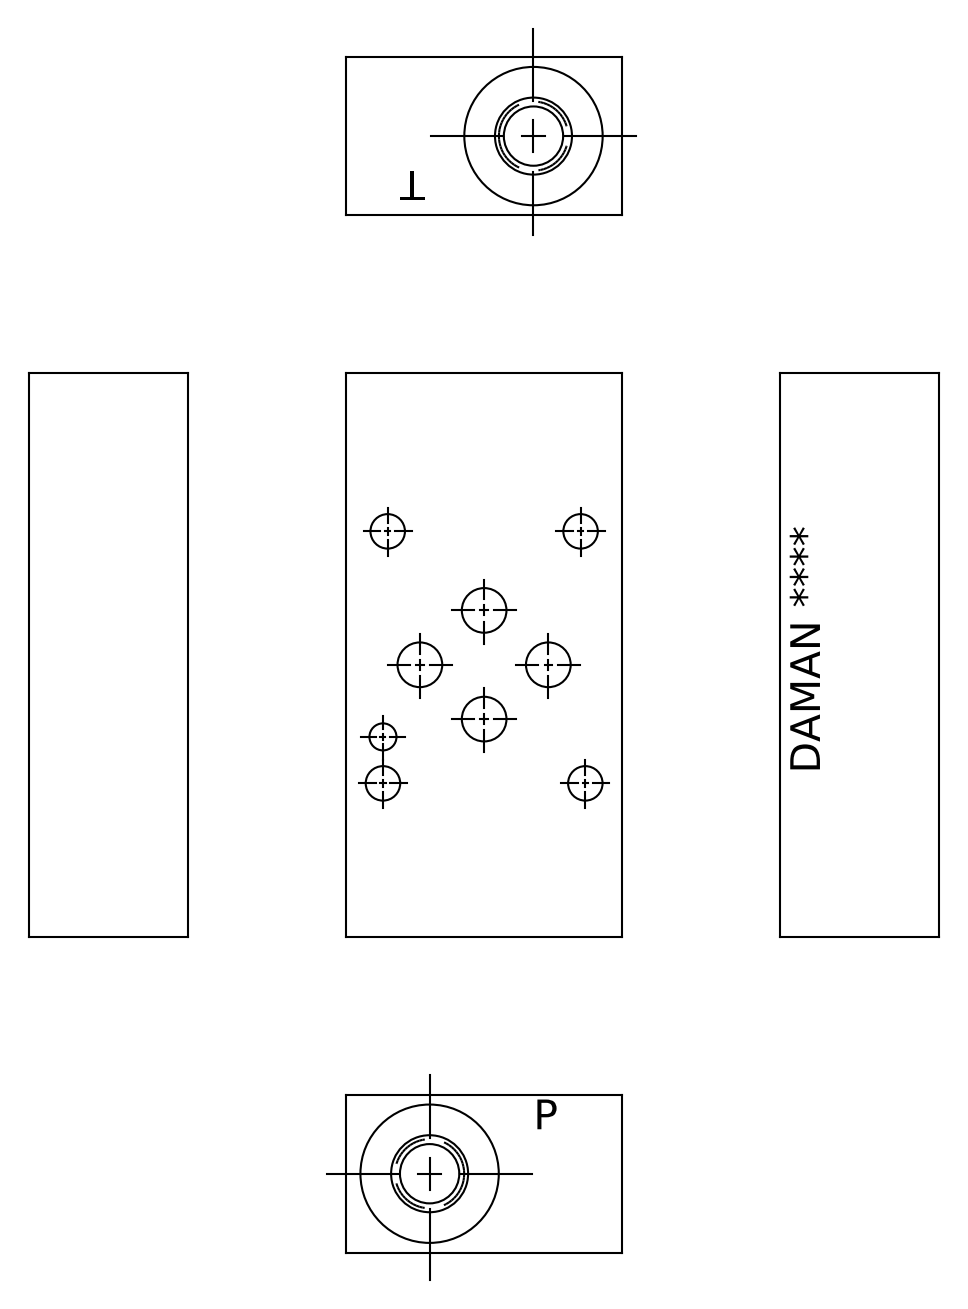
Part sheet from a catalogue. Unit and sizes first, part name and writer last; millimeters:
Units: millimetres
Overall size (bounding box): 90.5 × 44.45 × 25.4
Round holes (diameter × count): ⌀5.54 ×4, ⌀7.14 ×4, ⌀12.7 ×4, ⌀4.78 ×2, ⌀11.68 ×2, ⌀13.26 ×2, ⌀22.12 ×2, ⌀3.17 ×1, ⌀3.96 ×1
Main face-to-face distances: 25.4, 44.45, 90.5, 0.79, 89.71, 24.08, 1.32, 88.92, 44.41, 12.57
Hole centre spacings: 13.52, 13.53, 22.05, 33.55, 40.5, 51.45, 7.5, 12.99
Volume: 93 396 mm³ · Surface area: 18 552 mm²
Bodies: 1 solid, 398 faces (273 planar, 26 cylindrical, 99 other)
Part name (STEP PRODUCT): Part_AD03TPPT4B.B01850R1_3D
STEP written by: Autodesk Inventor 2022 (AUTOMOTIVE_DESIGN)
